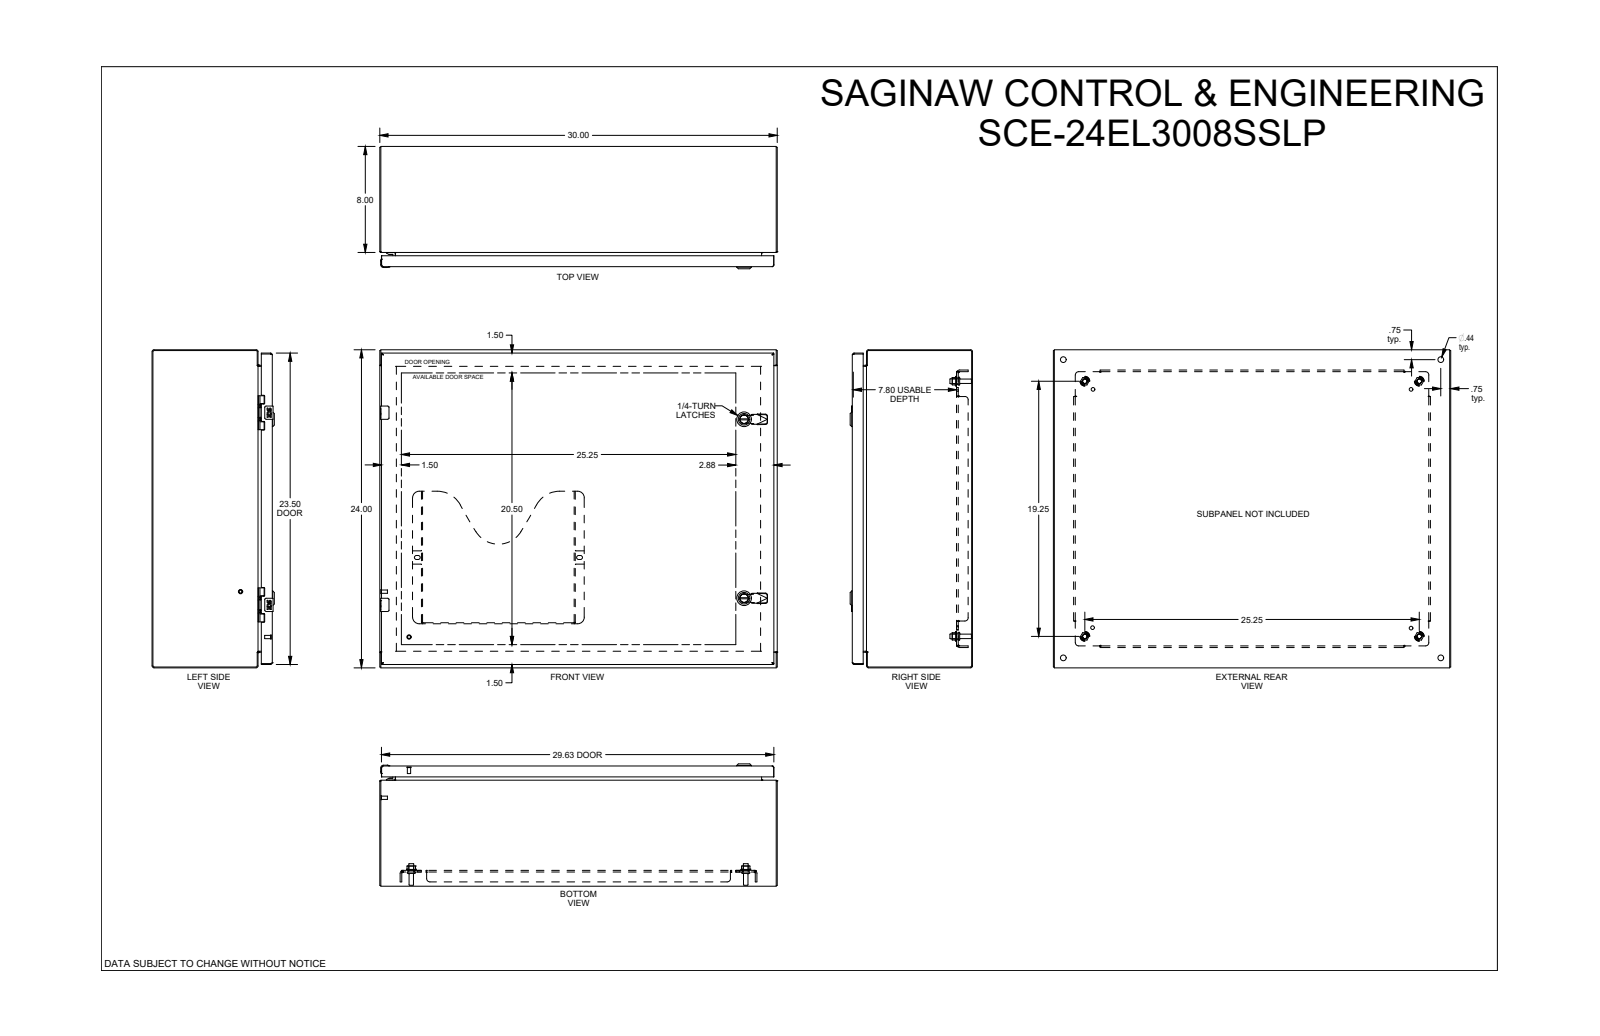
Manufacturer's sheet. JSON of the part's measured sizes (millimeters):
{"part_name": "SCE-24EL3008SSLP", "step_written_by": "SolidWorks 2019 (CONFIG_CONTROL_DESIGN)", "units": "millimeters", "bodies": {"solids": 0, "faces": 2838, "planar": 1307, "cylindrical": 759, "other": 772}, "overall_size": [762, 609.6, 234.4], "round_holes": [[4.4, 4], [5.2, 4], [6.2, 4], [6.8, 4], [7.1, 4], [9.3, 4], [9.5, 4], [11.1, 4], [12.7, 4], [4, 2], [5, 2], [5.5, 2]], "round_bosses_or_shafts": [[4.3, 6], [9.3, 4], [8.4, 4], [6.4, 4], [6.3, 4], [5, 3], [28, 2], [22, 2]], "partial_cylinders_radius": [[0.3, 56], [0.4, 30], [0.3, 28], [1, 23], [0.5, 20], [0.7, 12], [1.8, 10], [3.7, 10]], "face_to_face_distances": [1.9, 1.9, 226.6, 228.5, 230.5, 228.5, 30.5, 200, 3.2, 25.4], "hole_center_spacings": [368.3, 25, 0.5, 22.2, 114.1, 473.5, 25, 58.4]}
